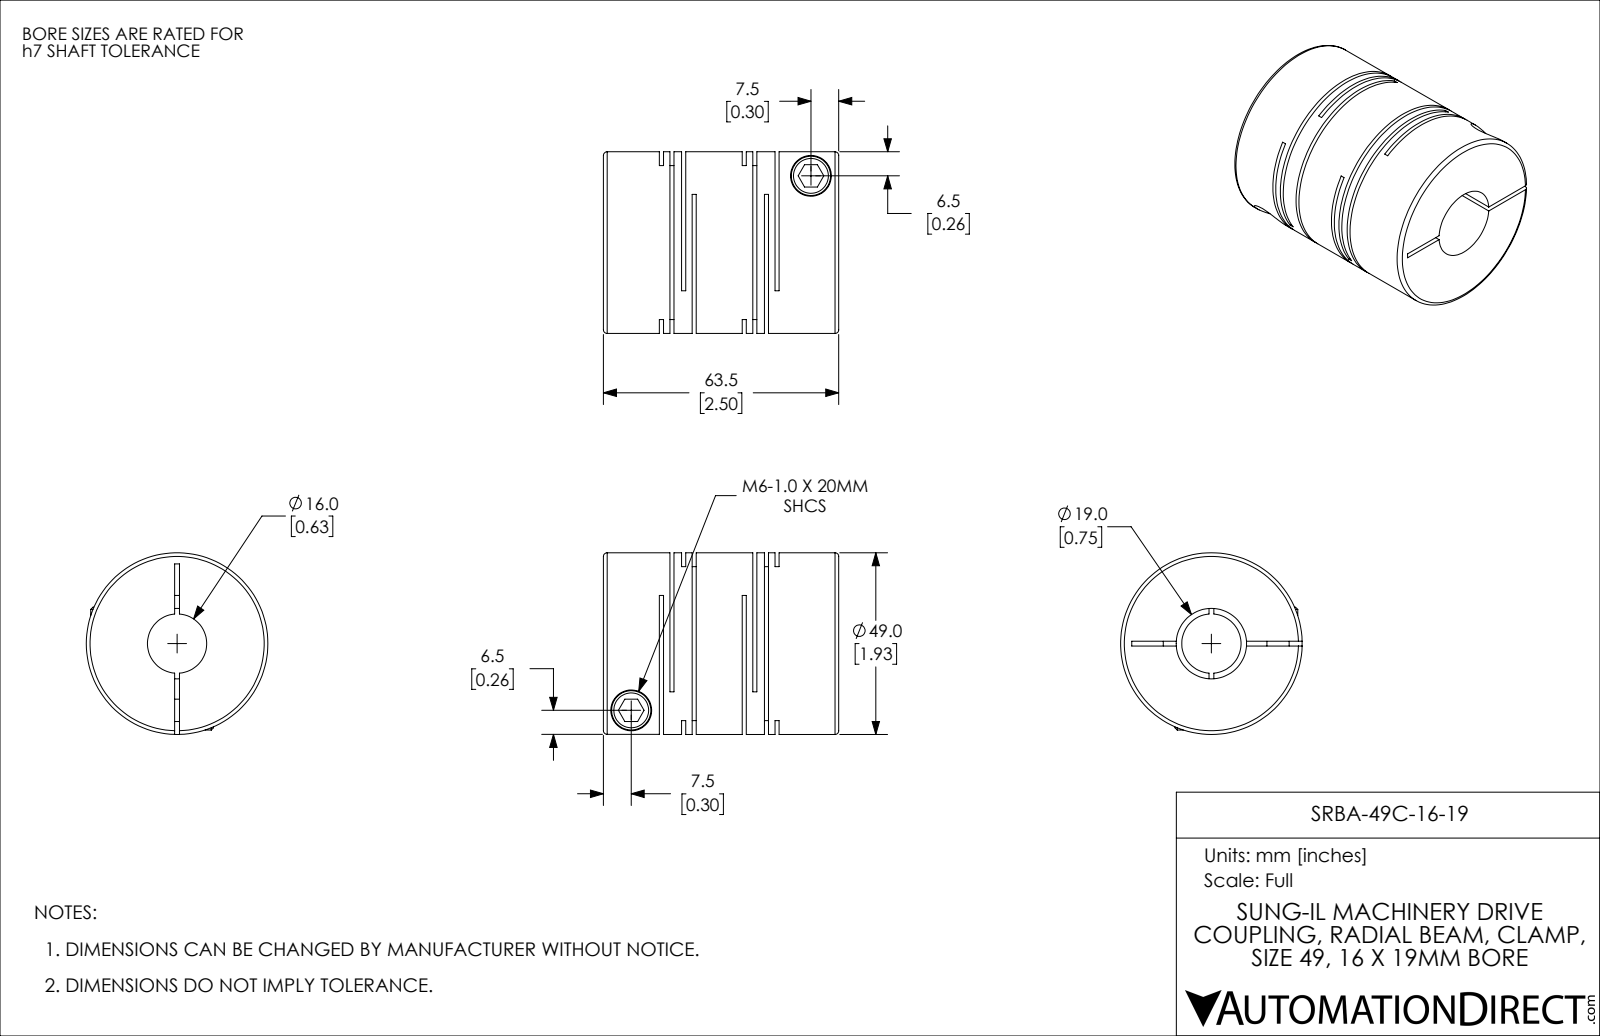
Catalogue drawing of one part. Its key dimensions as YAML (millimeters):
part_name: "SRBA-49C-16-19"
step_written_by: "SolidWorks 2021 (CONFIG_CONTROL_DESIGN)"
units: millimeters
bodies: {solids: 1, faces: 114, planar: 60, cylindrical: 42, other: 12}
overall_size: [63.5, 49, 49]
volume: 89051
surface_area: 38511
round_holes:
  - {diameter: 6, count: 2}
  - {diameter: 11, count: 2}
  - {diameter: 16, count: 1}
  - {diameter: 19, count: 1}
round_bosses_or_shafts:
  - {diameter: 10.6, count: 2}
  - {diameter: 49, count: 1}
face_to_face_distances: [6, 1.1, 22.35, 2.85, 1.75, 4.9, 21.25, 3.15, 19.5, 16.35]
